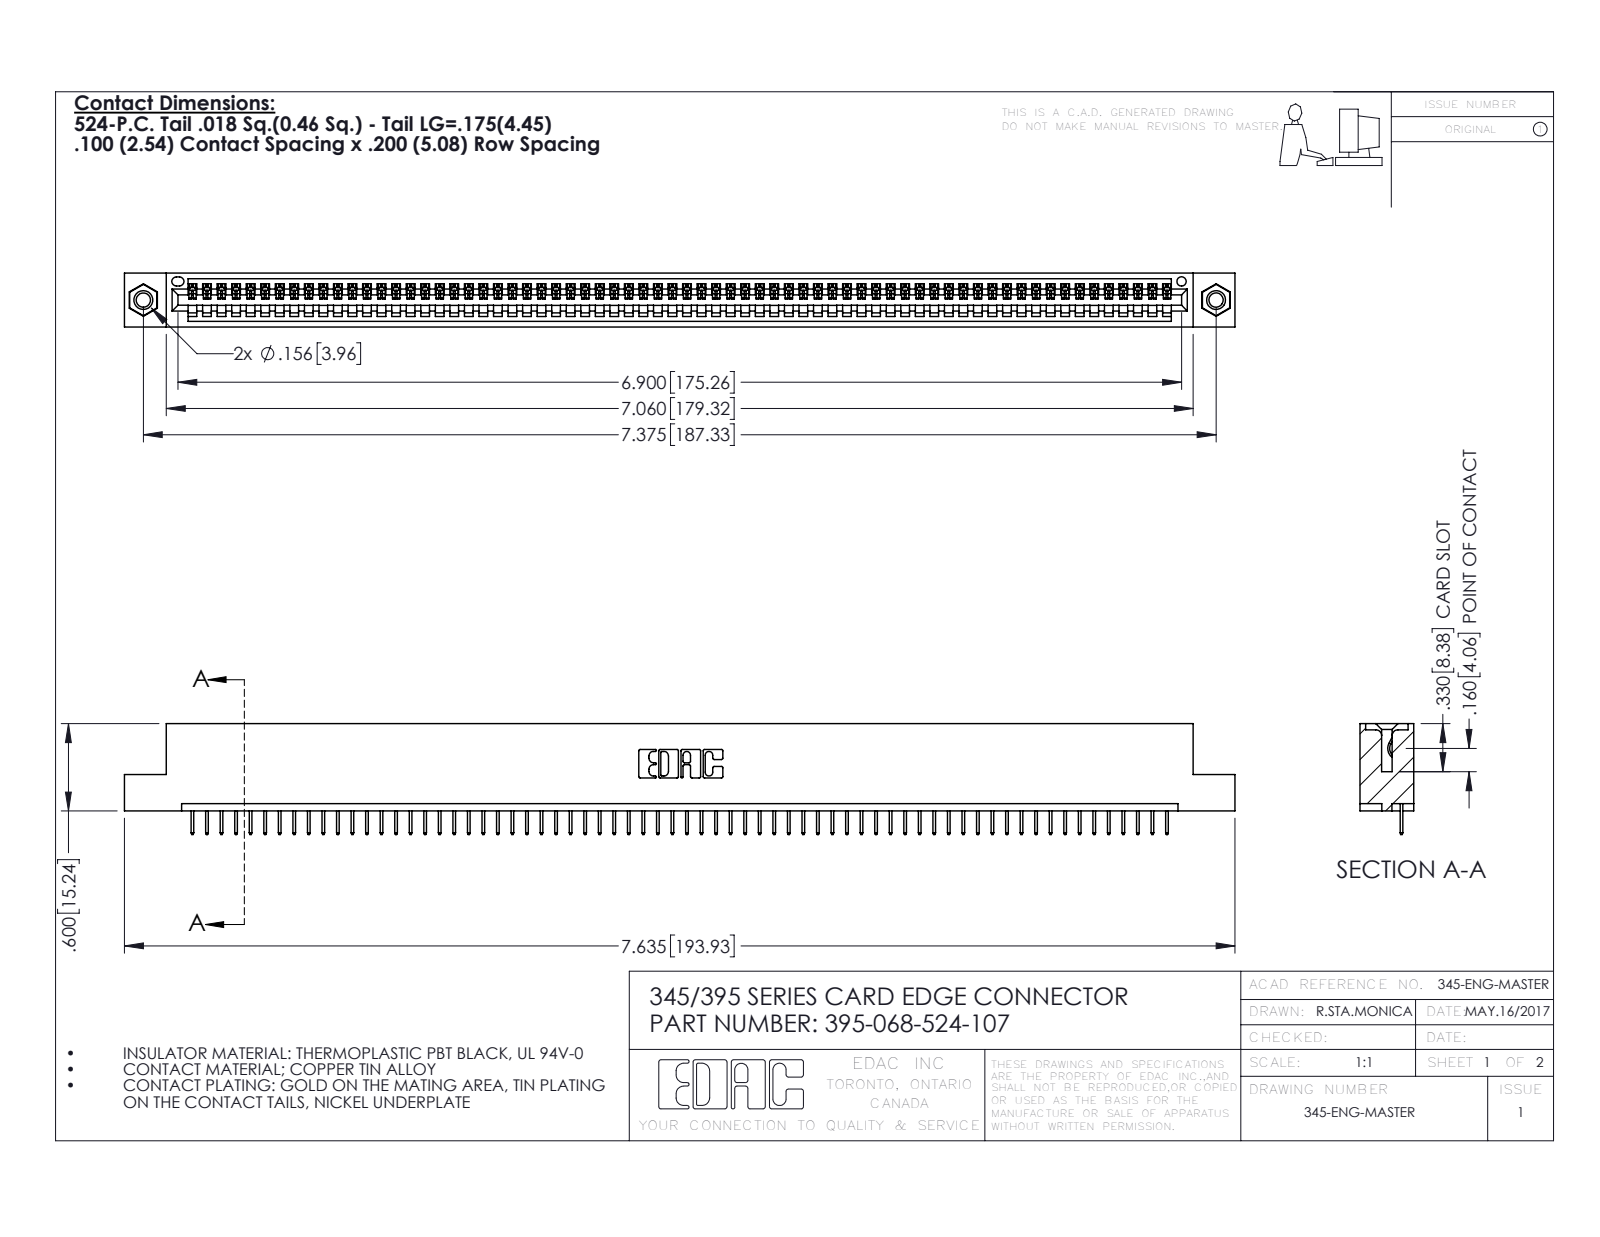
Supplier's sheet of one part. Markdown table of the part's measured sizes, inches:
| quantity | value |
| --- | --- |
| part name | 395-068-524-107; 345-292-001_345-293-124; 345 Part_Flush Mounting Lugs - 0.156 Dia-TI; 345-250-001_345-250-005-103 |
| STEP written by | SolidWorks 2016 (CONFIG_CONTROL_DESIGN) |
| units | inches |
| bodies | 71 solids, 4402 faces (3240 planar, 1146 cylindrical, 16 other) |
| overall size | 7.635 × 0.762 × 0.37 |
| volume | 1.12 in³ |
| surface area | 37.07 in² |
| round holes (diameter × count) | 0.098 × 2, 0.125 × 2, 0.156 × 2, 0.064 × 1 |
| round bosses / shafts (diameter × count) | 0.155 × 2 |
| partial cylindrical surfaces (radius × count) | 0.006 × 136, 0.01 × 22, 0.007 × 6, 0.031 × 6, 0.026 × 3, 0.031 × 2, 0.04 × 2, 0.014 × 1 |
| main face-to-face distances | 0.072, 0.298, 0.37, 0.2, 0.098, 0.272, 0.025, 0.225, 0.072, 0.149 |
| hole center spacings | 0.27, 7.139, 7.375 |
